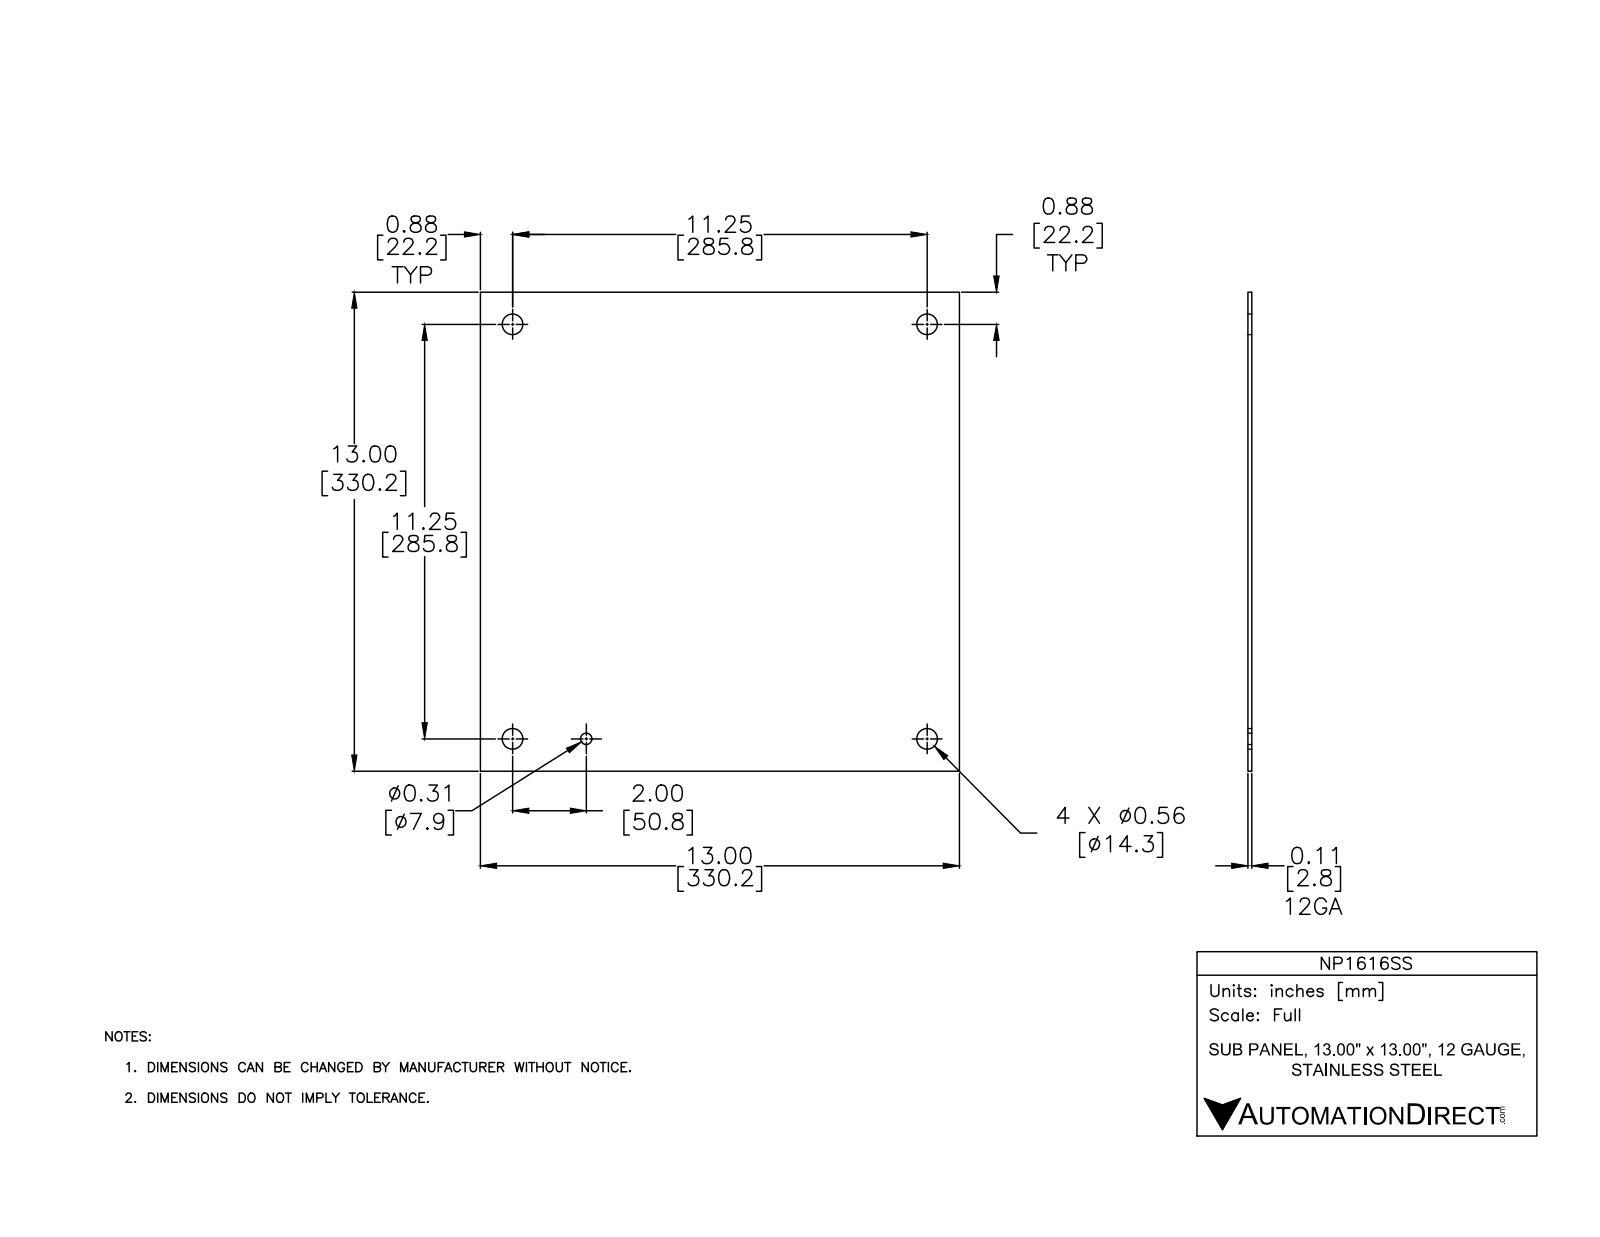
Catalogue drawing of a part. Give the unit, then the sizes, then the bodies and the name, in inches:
Units: inches
Overall size (bounding box): 13 × 13 × 0.094
Round holes (diameter × count): ⌀0.563 ×4, ⌀0.31 ×1
Main face-to-face distances: 0.094, 13
Hole centre spacings: 11.25, 2, 9.25, 11.25, 11.426, 14.564, 15.91, 15.91
Volume: 15.73 in³ · Surface area: 341.5 in²
Bodies: 1 solid, 11 faces (6 planar, 5 cylindrical, 0 other)
Part name (STEP PRODUCT): NP1616SS
STEP written by: Autodesk Inventor 2012 (AUTOMOTIVE_DESIGN)
